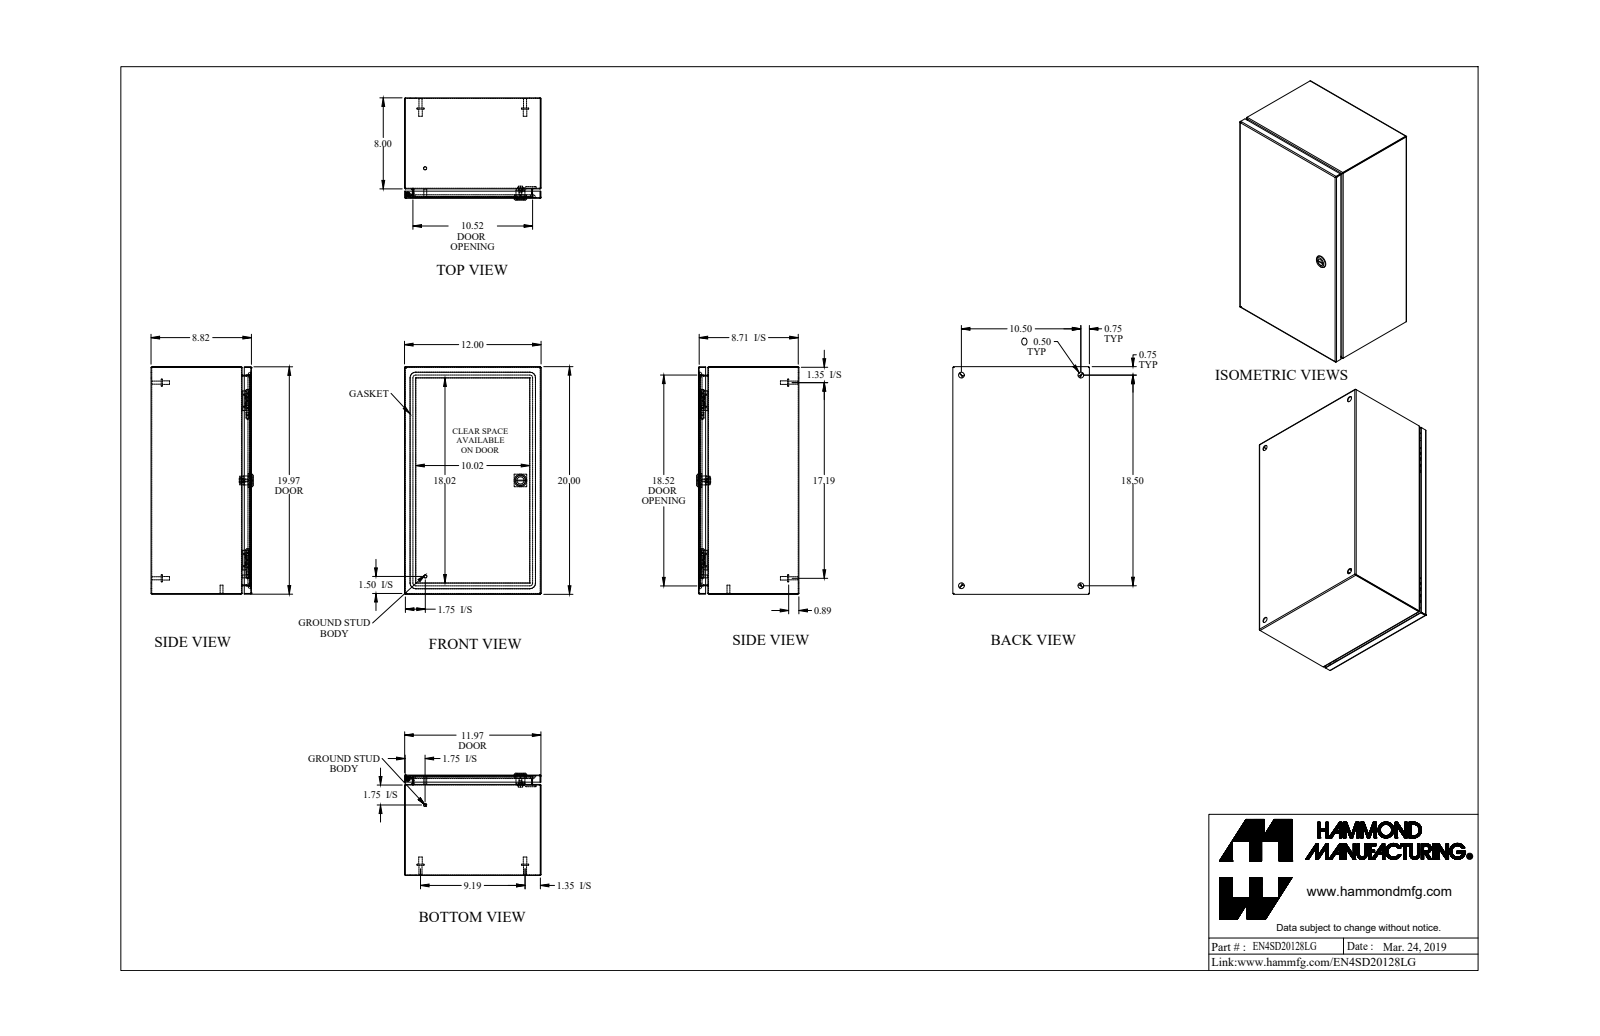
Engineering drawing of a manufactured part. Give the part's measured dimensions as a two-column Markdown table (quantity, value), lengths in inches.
| quantity | value |
| --- | --- |
| part name | EN4SD20128LG_Default |
| STEP written by | SolidWorks 2019 (CONFIG_CONTROL_DESIGN) |
| units | inches |
| bodies | 21 solids, 634 faces (285 planar, 213 cylindrical, 136 other) |
| overall size | 20 × 12 × 8.982 |
| volume | 70.07 in³ |
| surface area | 2 376 in² |
| round holes (diameter × count) | 0.5 × 4, 0.172 × 1, 0.232 × 1, 0.24 × 1, 0.242 × 1, 0.625 × 1, 0.785 × 1 |
| round bosses / shafts (diameter × count) | 0.625 × 4, 0.313 × 4, 0.27 × 4, 0.281 × 2, 0.25 × 2, 1.1 × 1, 0.525 × 1, 0.455 × 1 |
| partial cylindrical surfaces (radius × count) | 0.029 × 21, 0.086 × 21, 0.25 × 16, 19 × 8, 0.006 × 4, 0.062 × 4, 0.499 × 4, 0.125 × 2 |
| main face-to-face distances | 0.057, 8.765, 11.943, 8.708, 8.822, 19.943, 11.886, 12, 19.886, 20 |
| hole center spacings | 10.5, 18.5, 21.272, 9.31, 9.311, 13.217, 13.217 |
